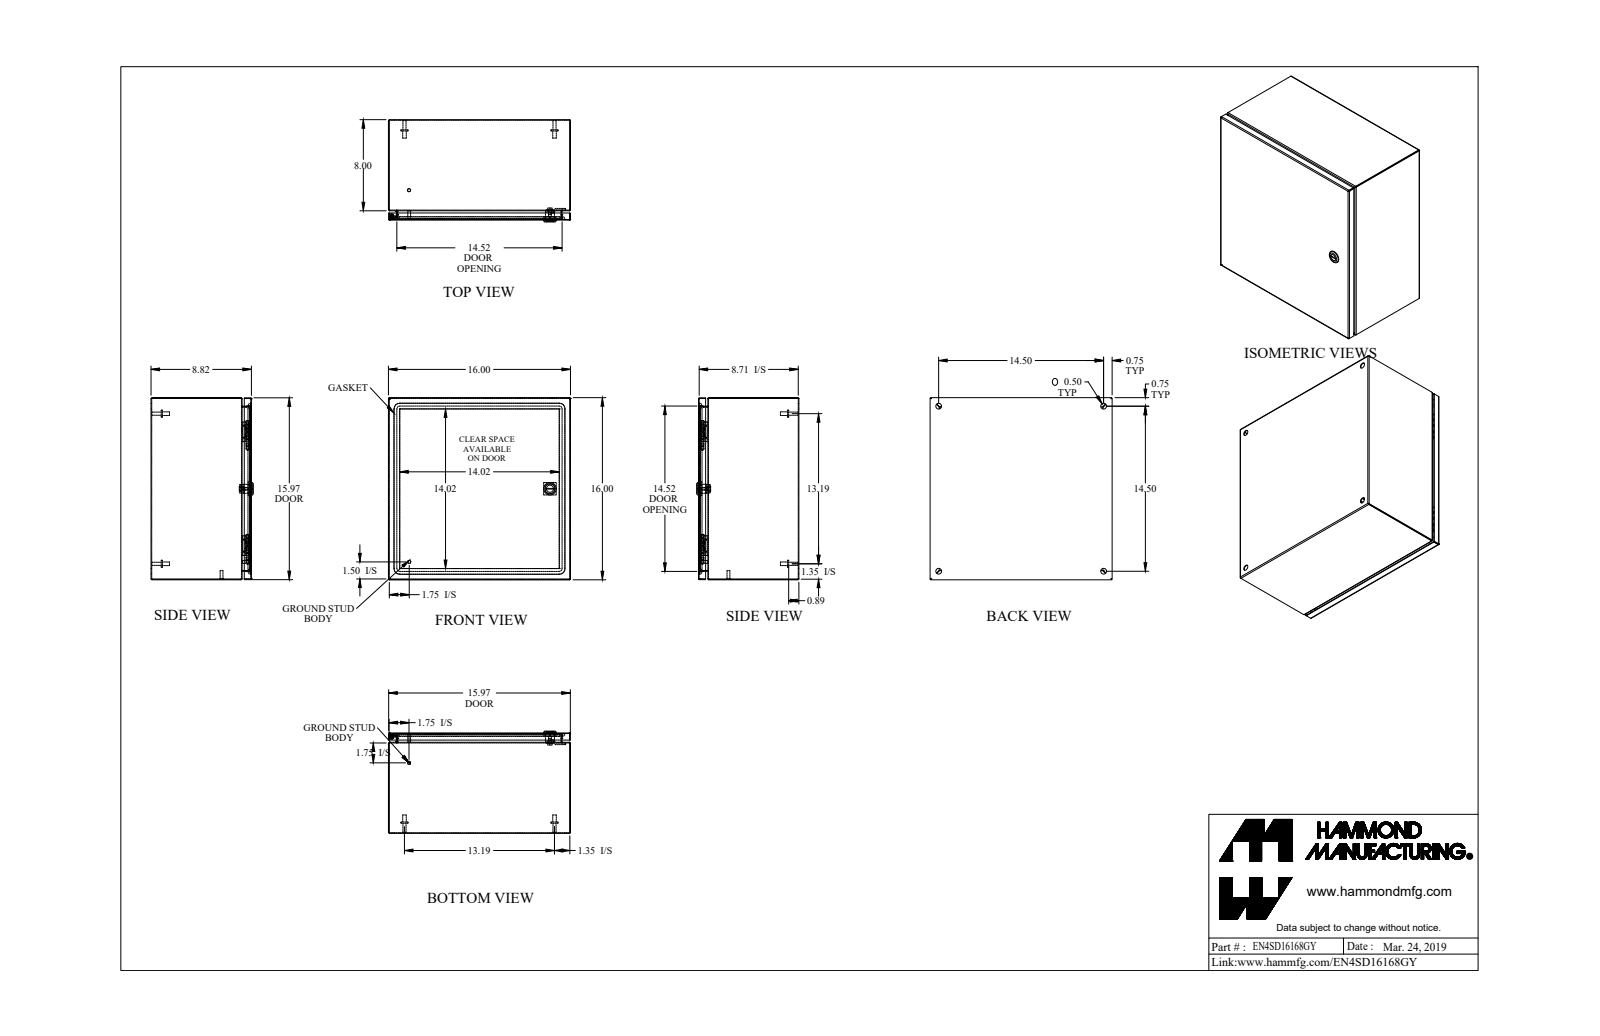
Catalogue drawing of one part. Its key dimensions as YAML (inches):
part_name: "EN4SD16168GY_Default"
step_written_by: "SolidWorks 2019 (CONFIG_CONTROL_DESIGN)"
units: inches
bodies: {solids: 21, faces: 634, planar: 285, cylindrical: 213, other: 136}
overall_size: [16, 16, 8.982]
volume: 71.9
surface_area: 2440
round_holes:
  - {diameter: 0.5, count: 4}
  - {diameter: 0.172, count: 1}
  - {diameter: 0.232, count: 1}
  - {diameter: 0.24, count: 1}
  - {diameter: 0.242, count: 1}
  - {diameter: 0.625, count: 1}
  - {diameter: 0.785, count: 1}
round_bosses_or_shafts:
  - {diameter: 0.625, count: 4}
  - {diameter: 0.313, count: 4}
  - {diameter: 0.27, count: 4}
  - {diameter: 0.281, count: 2}
  - {diameter: 0.25, count: 2}
  - {diameter: 1.1, count: 1}
  - {diameter: 0.525, count: 1}
  - {diameter: 0.455, count: 1}
partial_cylinders:
  - {radius: 0.029, count: 21}
  - {radius: 0.086, count: 21}
  - {radius: 0.25, count: 16}
  - {radius: 19, count: 8}
  - {radius: 0.006, count: 4}
  - {radius: 0.062, count: 4}
  - {radius: 0.499, count: 4}
  - {radius: 0.125, count: 2}
face_to_face_distances: [0.057, 8.765, 15.943, 15.886, 8.708, 8.822, 16, 0.822, 7.943, 0.749]
hole_center_spacings: [14.5, 20.506, 7.326, 7.327, 15.271, 15.272]
